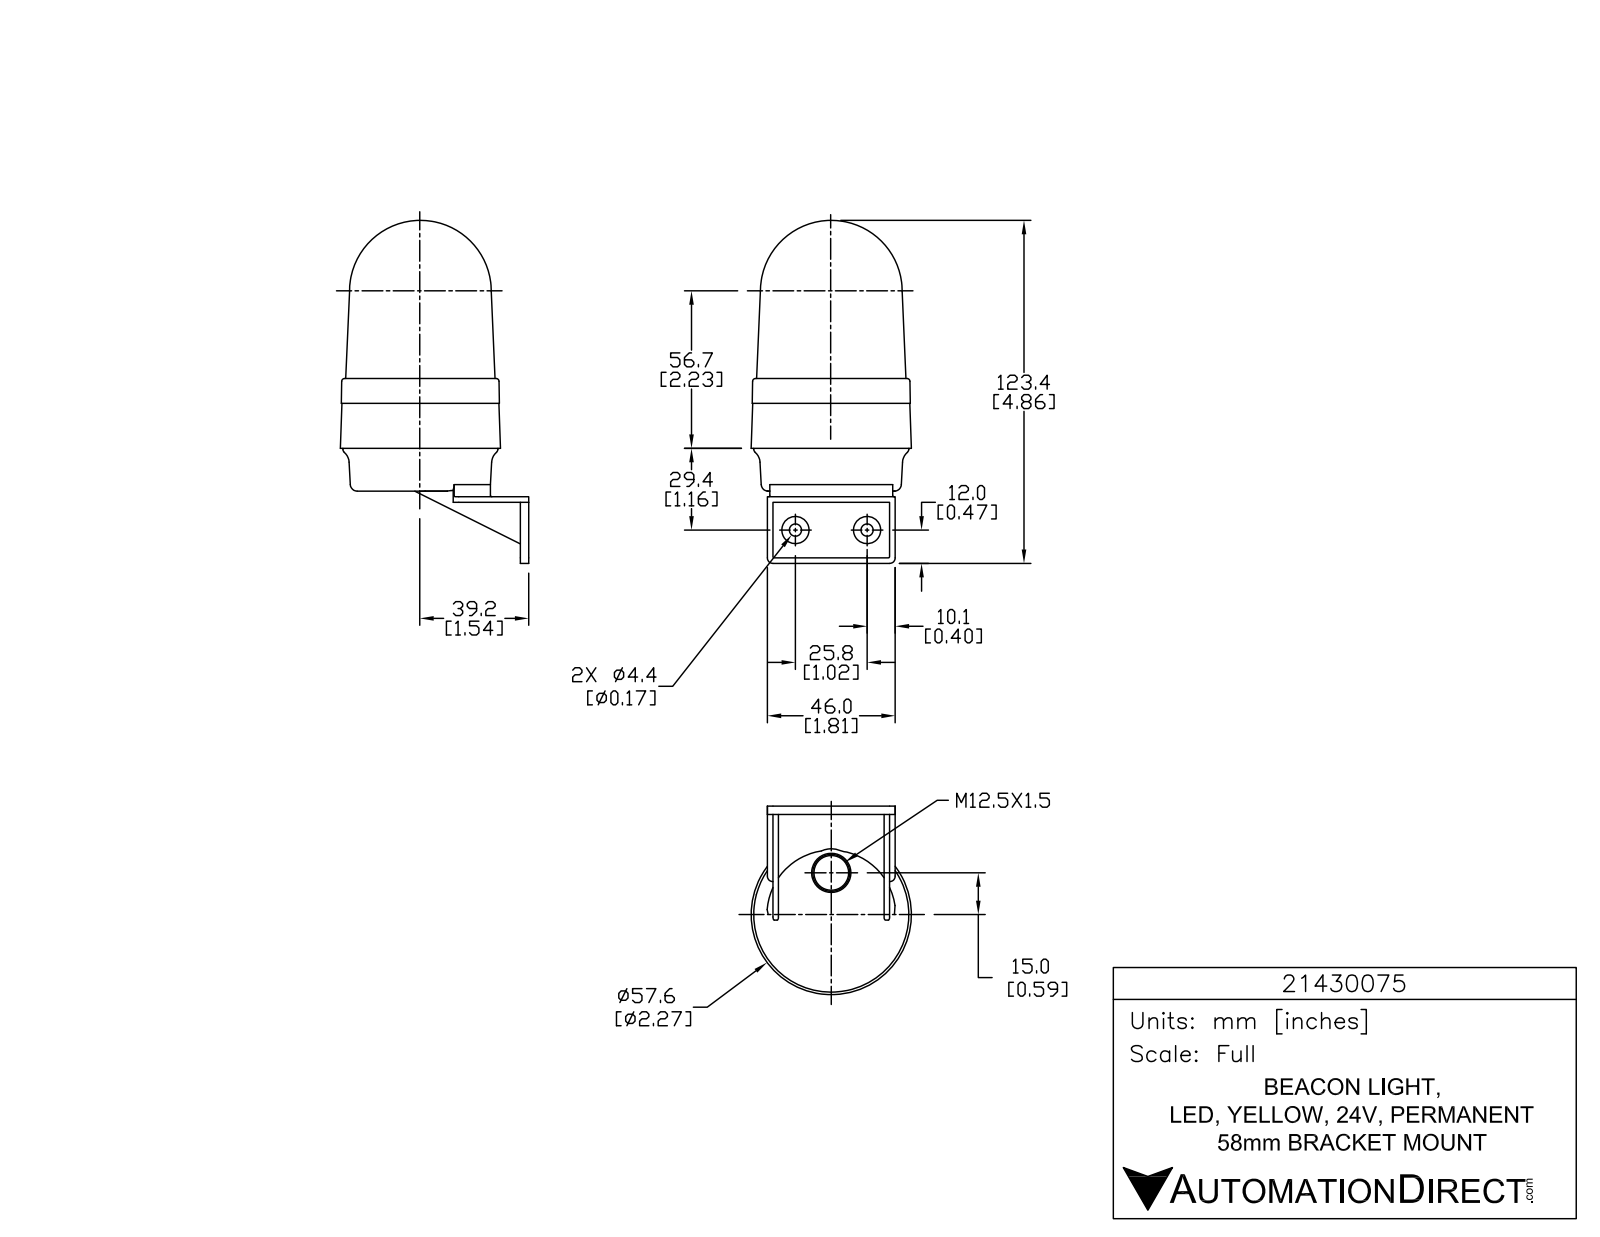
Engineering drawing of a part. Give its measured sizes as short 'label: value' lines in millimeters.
name: 21430075
written by: SolidWorks 2015 (AUTOMOTIVE_DESIGN)
unit: mm
bodies: 1 solid, 828 faces (551 planar, 179 cylindrical, 98 other)
size: 123.4 × 72.4 × 61.1
volume: 203 700 mm³; area: 24 190 mm²
holes: 3× ⌀1, 2× ⌀4.4
bosses: 3× ⌀5.7, 3× ⌀1.4, 2× ⌀9.8, 1× ⌀55.8
rounds: 6× R0.2, 6× R0.2, 6× R0.2, 6× R0.5, 6× R3.3, 4× R2, 3× R0.1, 3× R0.1
face distances: 2, 4, 40, 42, 1, 3, 38, 22, 24, 19.4
hole spacings: 25.8
